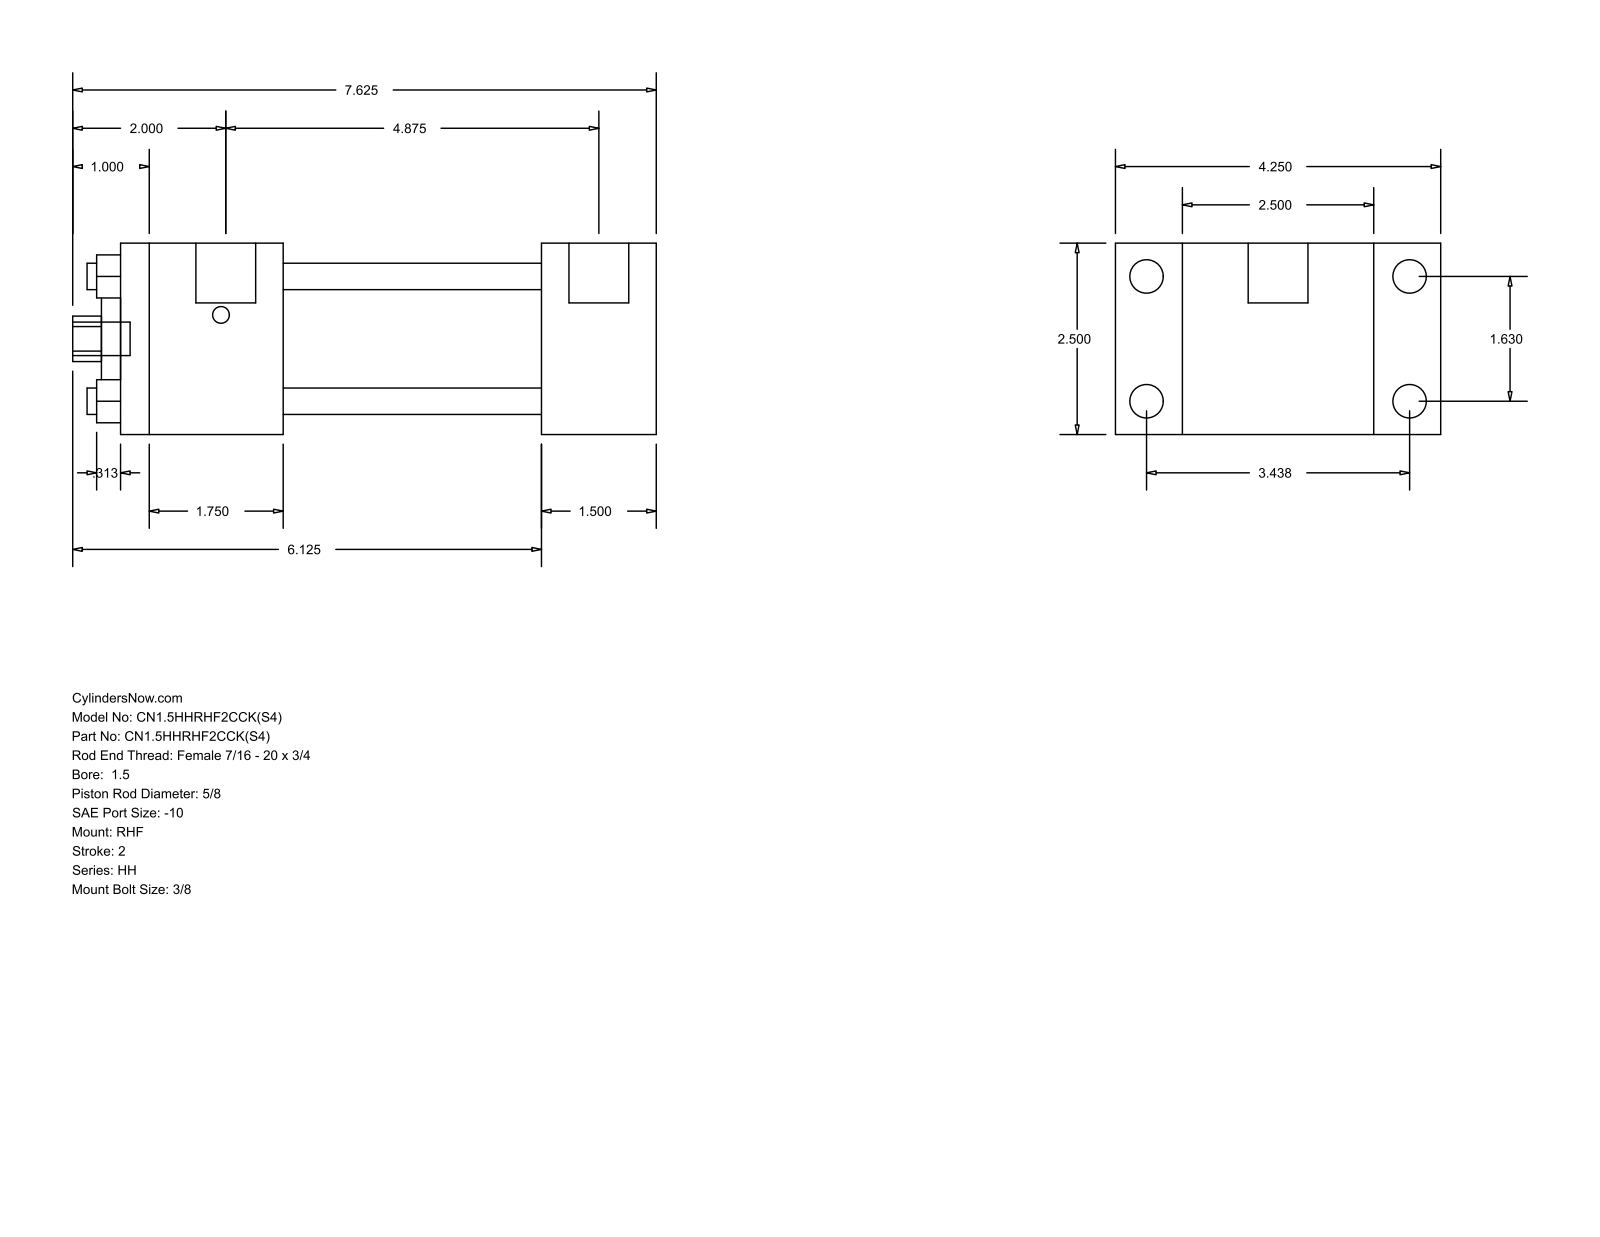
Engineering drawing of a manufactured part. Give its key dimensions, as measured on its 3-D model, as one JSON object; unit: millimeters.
{"part_name": "HH_RHF__0150_0.625", "step_written_by": "GSSL Pune (CONFIG_CONTROL_DESIGN)", "units": "millimeters", "bodies": {"solids": 0, "faces": 88, "planar": 60, "cylindrical": 28, "other": 0}, "overall_size": [193.68, 107.95, 63.5], "round_holes": [[8.76, 4], [15.88, 1], [28.57, 1], [44.45, 1]], "round_bosses_or_shafts": [[11.13, 4], [5.56, 4], [19.84, 2], [11.11, 1]], "partial_cylinders_radius": [[7.54, 1]], "face_to_face_distances": [63.5, 22.23, 85.73, 38.11, 139.69, 177.8, 107.96, 85.72, 53.97, 123.83], "hole_center_spacings": [29.27, 41.4, 58.55]}
